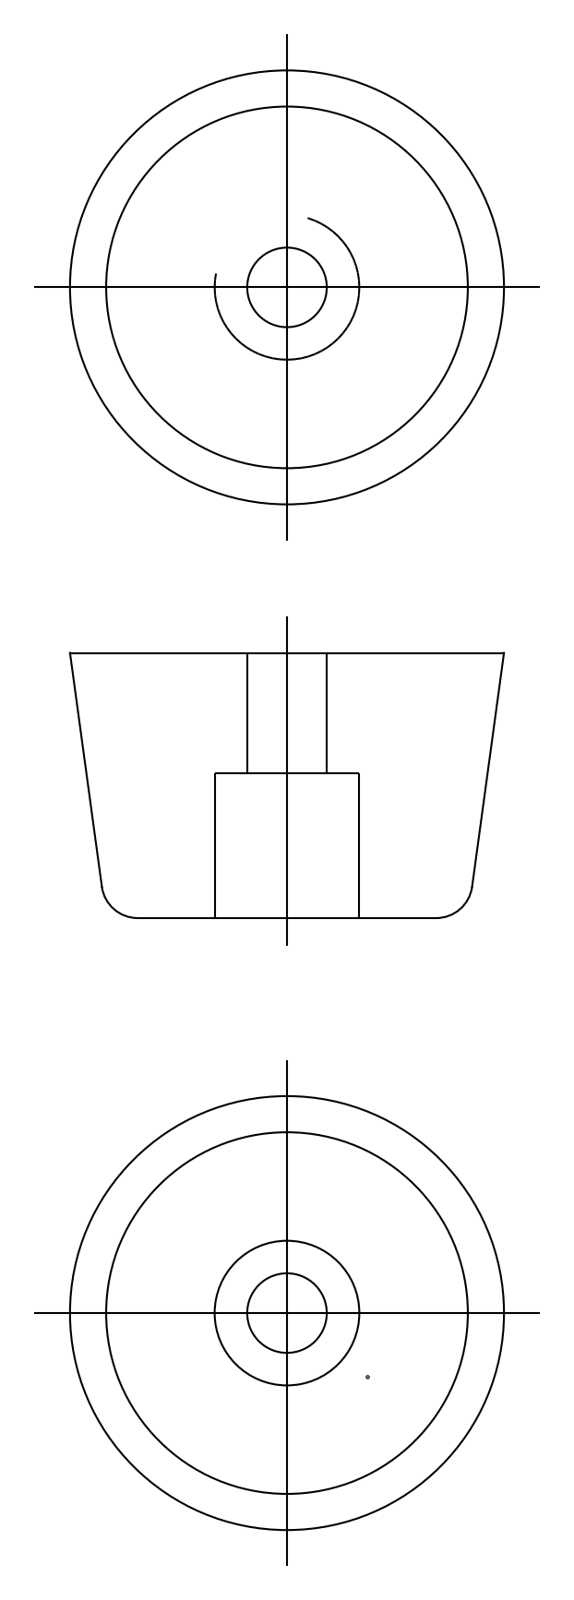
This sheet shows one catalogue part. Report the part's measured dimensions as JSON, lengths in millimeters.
{"step_written_by": "spGate 19.8.4 (****-****-****-****) (AUTOMOTIVE_DESIGN)", "units": "millimeters", "bodies": {"solids": 1, "faces": 11, "planar": 3, "cylindrical": 4, "other": 4}, "overall_size": [18, 18, 11], "volume_mm3": 2135, "surface_area_mm2": 1133, "round_holes": [[3.3, 1], [6, 1]], "face_to_face_distances": [11, 6, 5]}
